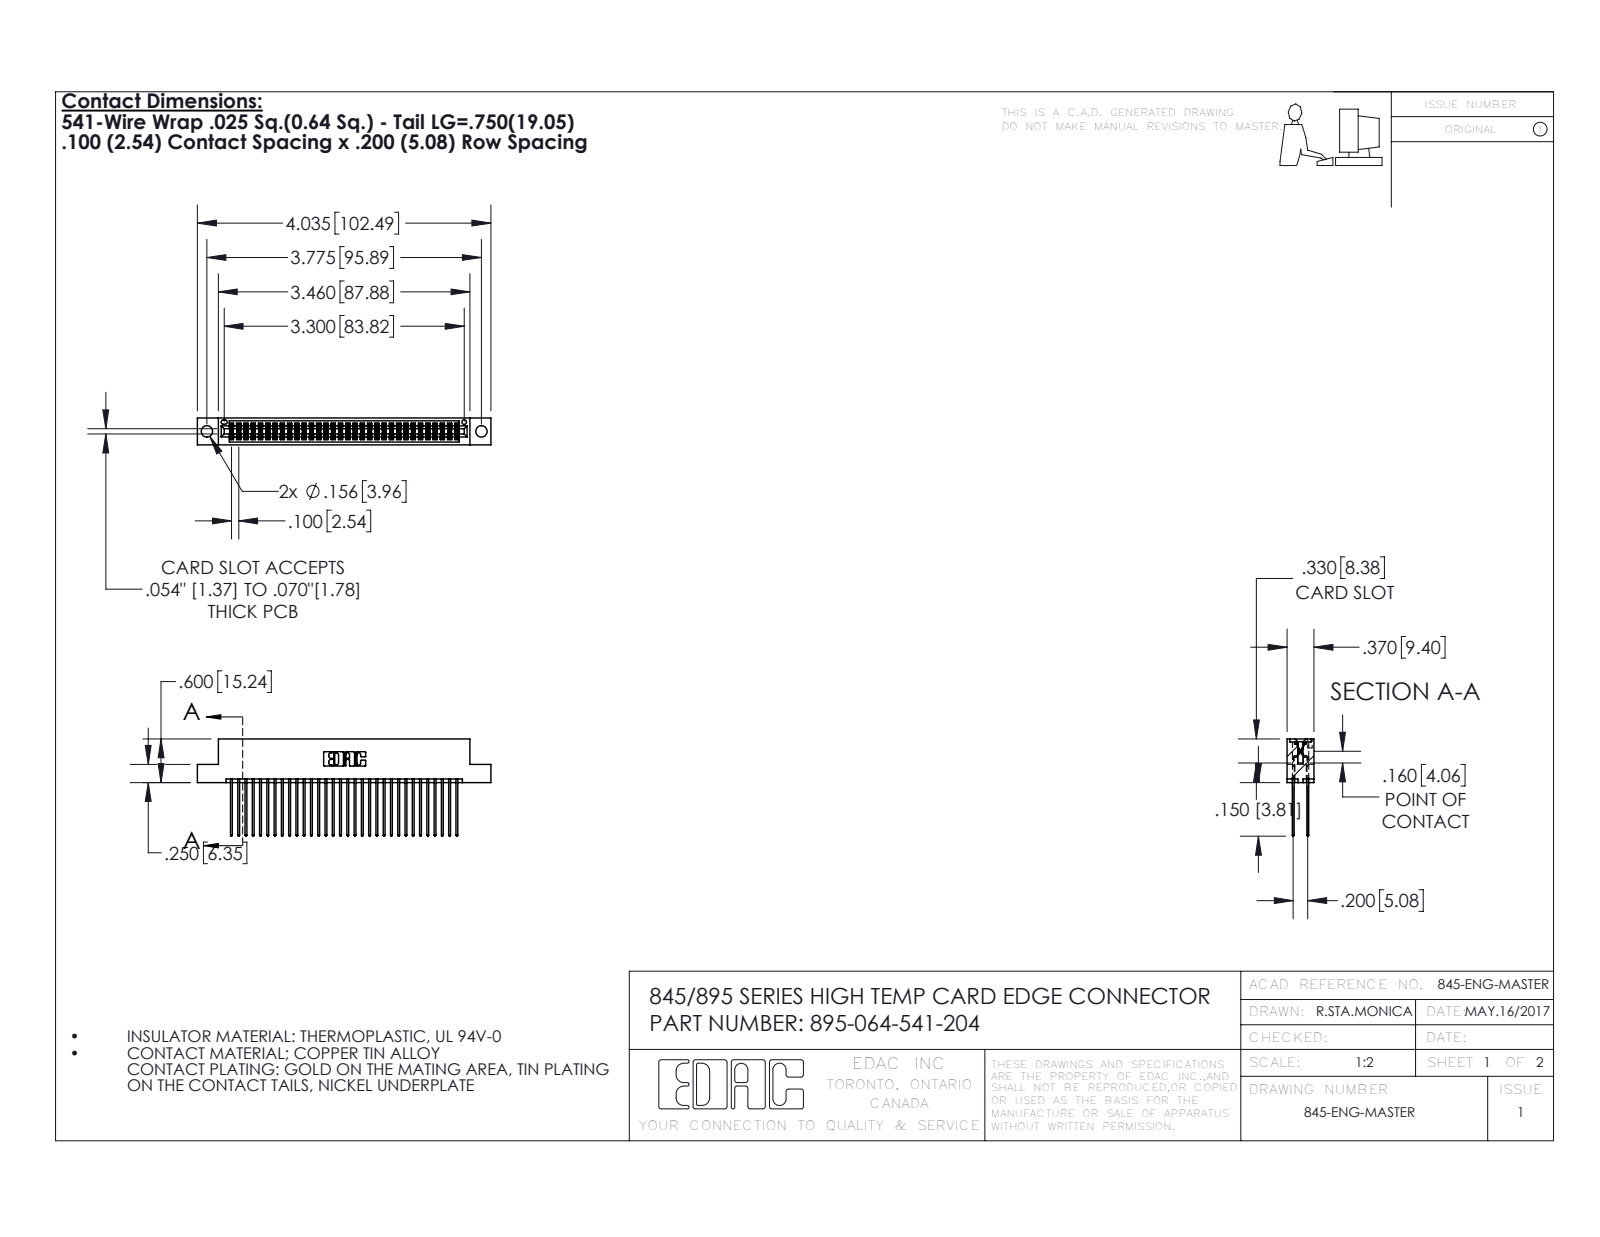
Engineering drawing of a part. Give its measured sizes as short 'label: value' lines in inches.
name: 395-064-541-204; 345-292-001_345-293-141; 345 Part_Flush Mounting Lugs - 0.156 Dia-TH
written by: SolidWorks 2016 (CONFIG_CONTROL_DESIGN)
unit: in
bodies: 65 solids, 3326 faces (2192 planar, 1134 cylindrical, 0 other)
size: 4.035 × 1.337 × 0.37
volume: 0.619 in³; area: 25.33 in²
holes: 2× ⌀0.156, 1× ⌀0.064
rounds: 96× R0.006, 64× R0.01, 22× R0.01, 6× R0.007, 6× R0.031, 3× R0.026, 2× R0.014, 2× R0.019
face distances: 0.298, 0.072, 0.2, 0.098, 0.272, 0.025, 0.225, 0.37, 0.175, 0.149
hole spacings: 0.27, 3.54, 3.775
